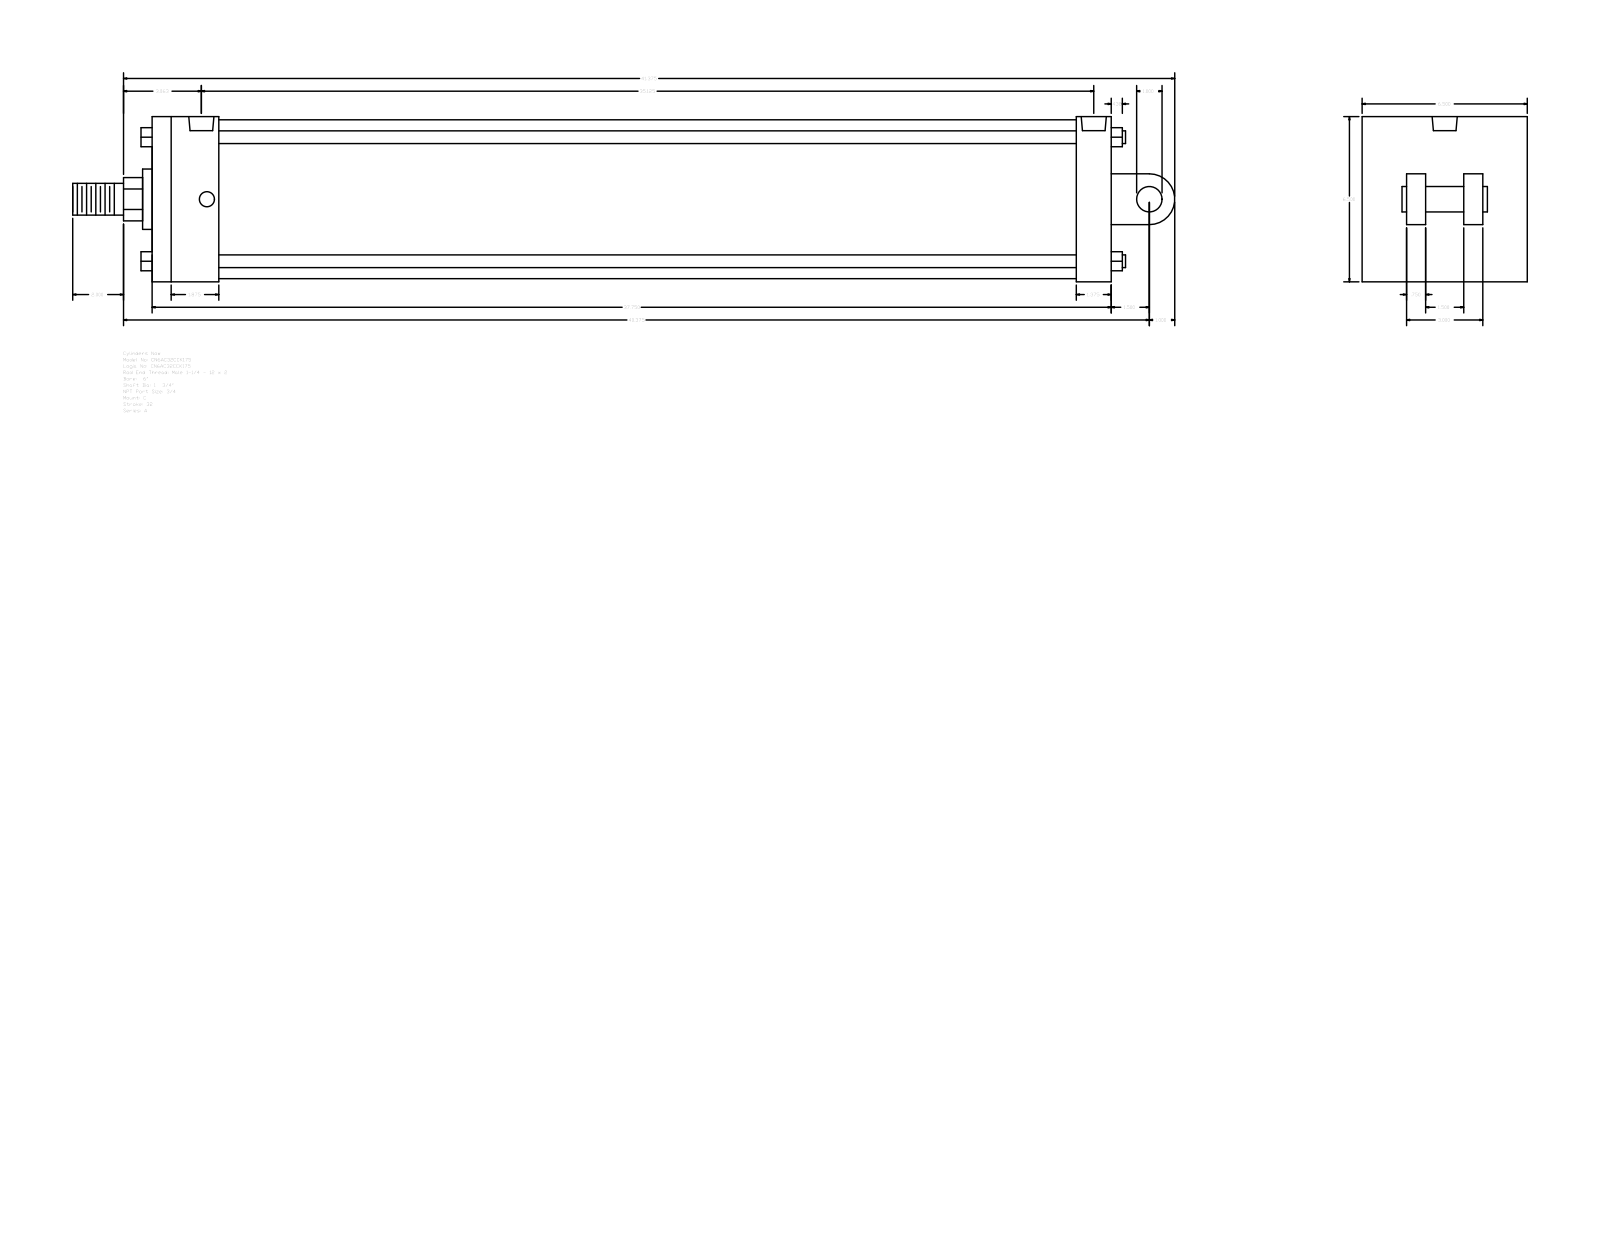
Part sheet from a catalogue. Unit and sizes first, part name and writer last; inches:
Units: inches
Overall size (bounding box): 43.375 × 6.5 × 6.5
Round holes (diameter × count): ⌀0.594 ×4, ⌀0.989 ×2
Round bosses / shafts (diameter × count): ⌀0.5 ×4, ⌀6.25 ×1, ⌀2.375 ×1, ⌀1.75 ×1, ⌀1.25 ×1, ⌀1 ×1
Partial cylindrical surfaces — rounded edges, fillets, slot ends (radius × count): R0.852 ×1, R1 ×1
Main face-to-face distances: 6.5, 37.75, 0.75, 2.25, 2.625, 35.125, 36.375, 33.75, 1.375, 2.5
Hole centre spacings: 0.219, 34.687, 34.906, 35.125
Bodies: 0 solids, 135 faces (102 planar, 33 cylindrical, 0 other)
Part name (STEP PRODUCT): A_C__0600_1.75
STEP written by: GSSL Pune (CONFIG_CONTROL_DESIGN)
